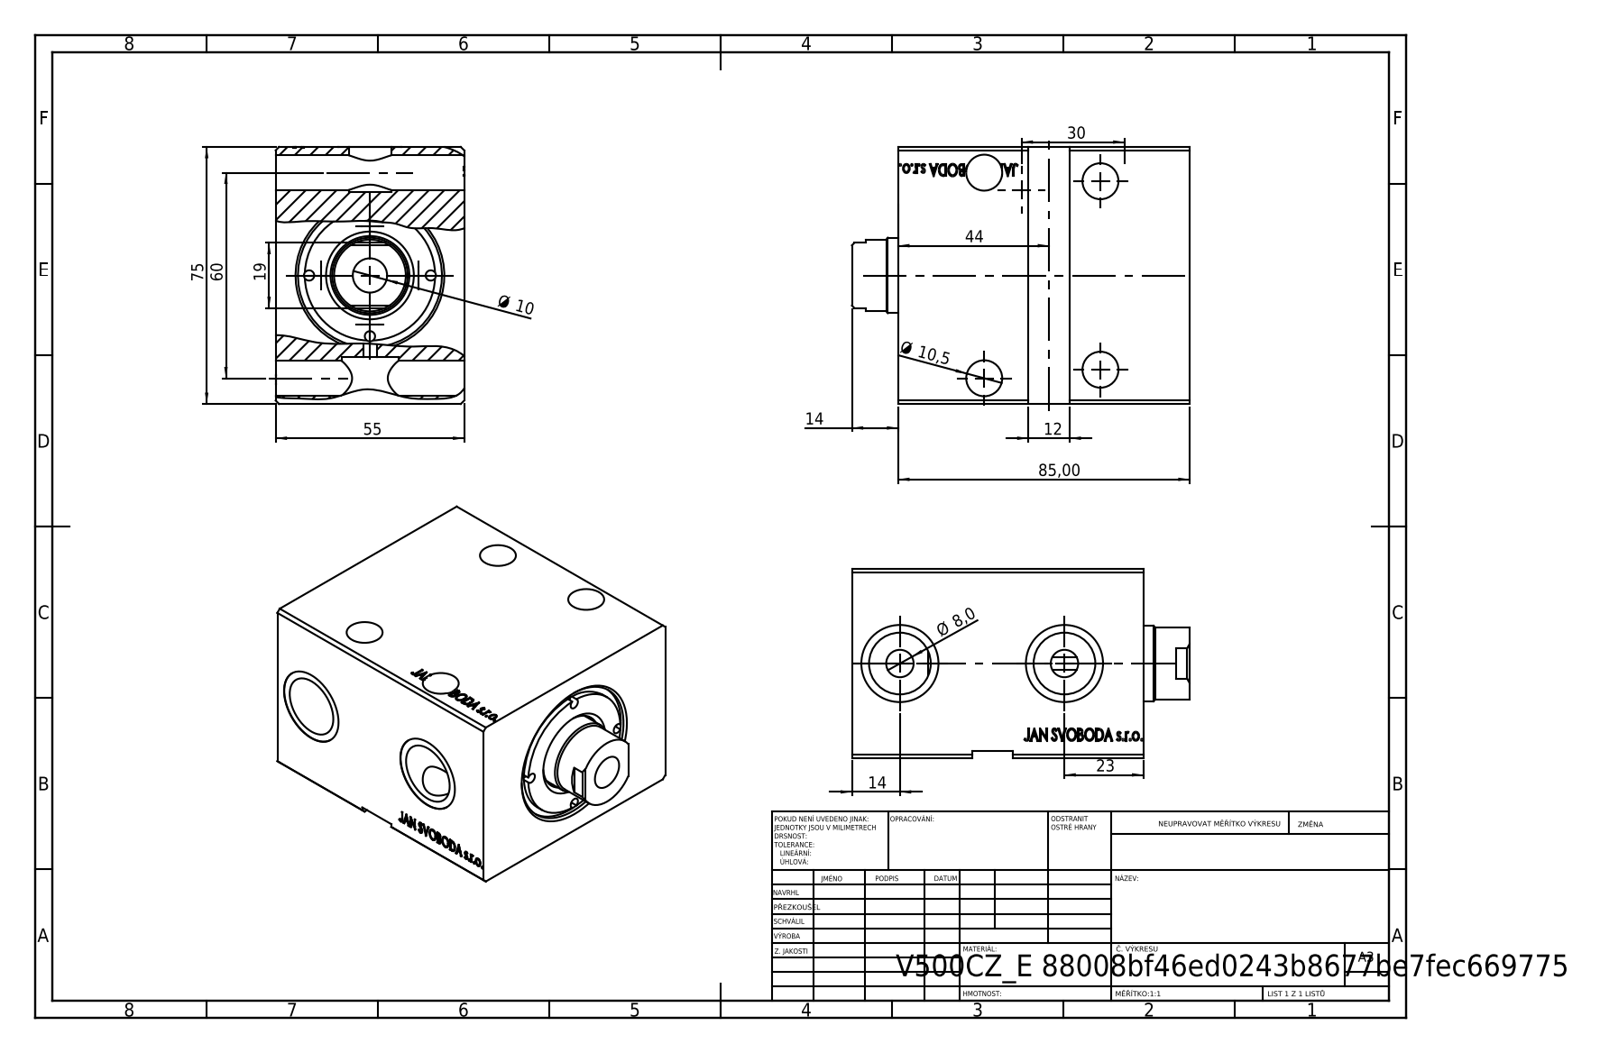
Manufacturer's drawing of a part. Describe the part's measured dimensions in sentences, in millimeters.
The part is named "V500CZ_VCP_E; V500CZ_E; V500CZ_VC_vysunovaci_E". Its 3-D file was written by "SolidWorks 2019 (CONFIG_CONTROL_DESIGN)". It is 3 solids with 800 faces: 381 planar, 67 cylindrical and 352 other. Overall it measures 98.5 by 75 by 55 millimeters. Its volume is 312 859 cubic millimeters and its surface area 57 055 square millimeters. Round holes: 4 of diameter 3, 4 of diameter 10.5, 4 of diameter 18, 4 of diameter 22.5, 2 of diameter 5.5, 2 of diameter 8, 1 of diameter 10, 1 of diameter 22, 1 of diameter 23, 1 of diameter 32, 1 of diameter 36, 1 of diameter 42. Round bosses or shafts: 1 of diameter 38, 1 of diameter 20.92. The main face-to-face distances are 55, 75, 85, 30, 84.8, 29.8, 11.8, 43.2, 73, 73.2. The hole center spacings are 17.75, 25.1, 34, 35.5, 66.75, 1, 3, 48.
